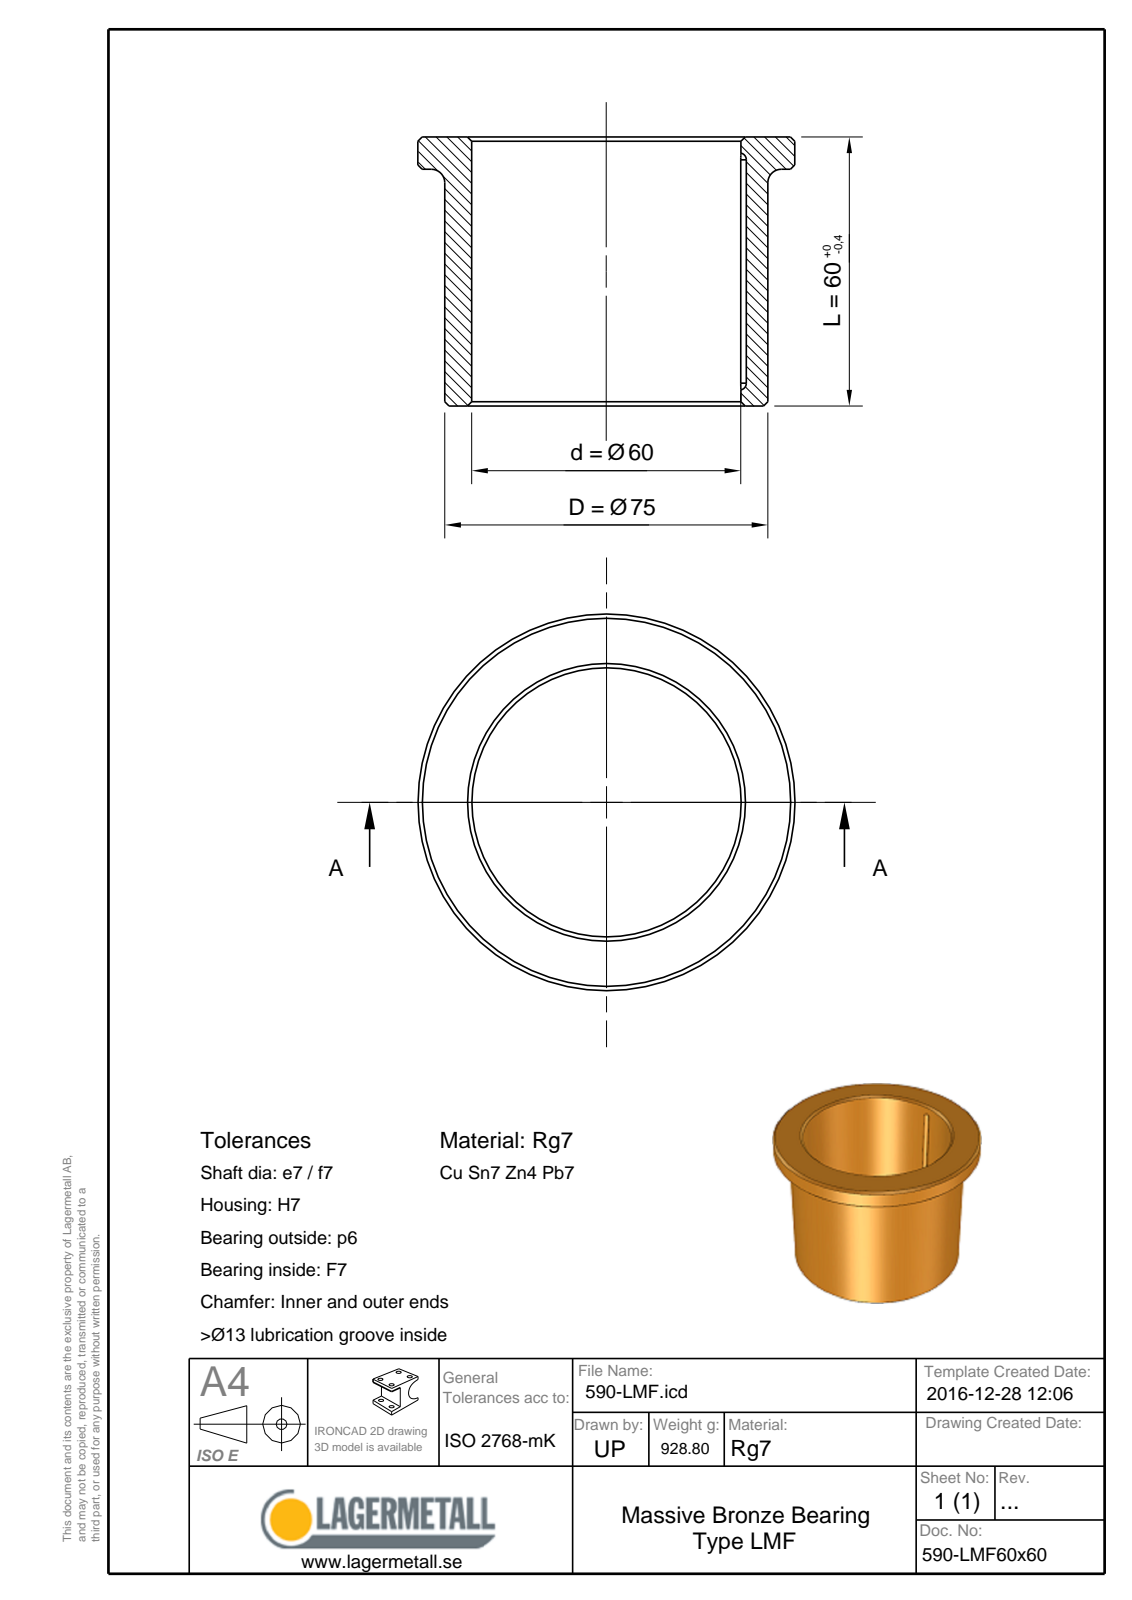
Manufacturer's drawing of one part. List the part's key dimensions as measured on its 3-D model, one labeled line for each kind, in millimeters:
Part name (STEP PRODUCT): 590-LMF60x60
STEP written by: Spatial InterOp 3D (CONFIG_CONTROL_DESIGN)
Units: millimetres
Bodies: 1 solid, 17 faces (4 planar, 5 cylindrical, 8 other)
Overall size (bounding box): 85 × 85 × 60
Volume: 105 539 mm³ · Surface area: 30 592 mm²
Round holes (diameter × count): ⌀60 ×1
Round bosses / shafts (diameter × count): ⌀85 ×1, ⌀75 ×1
Partial cylindrical surfaces — rounded edges, fillets, slot ends (radius × count): R1.75 ×2
Main face-to-face distances: 60, 52, 8
